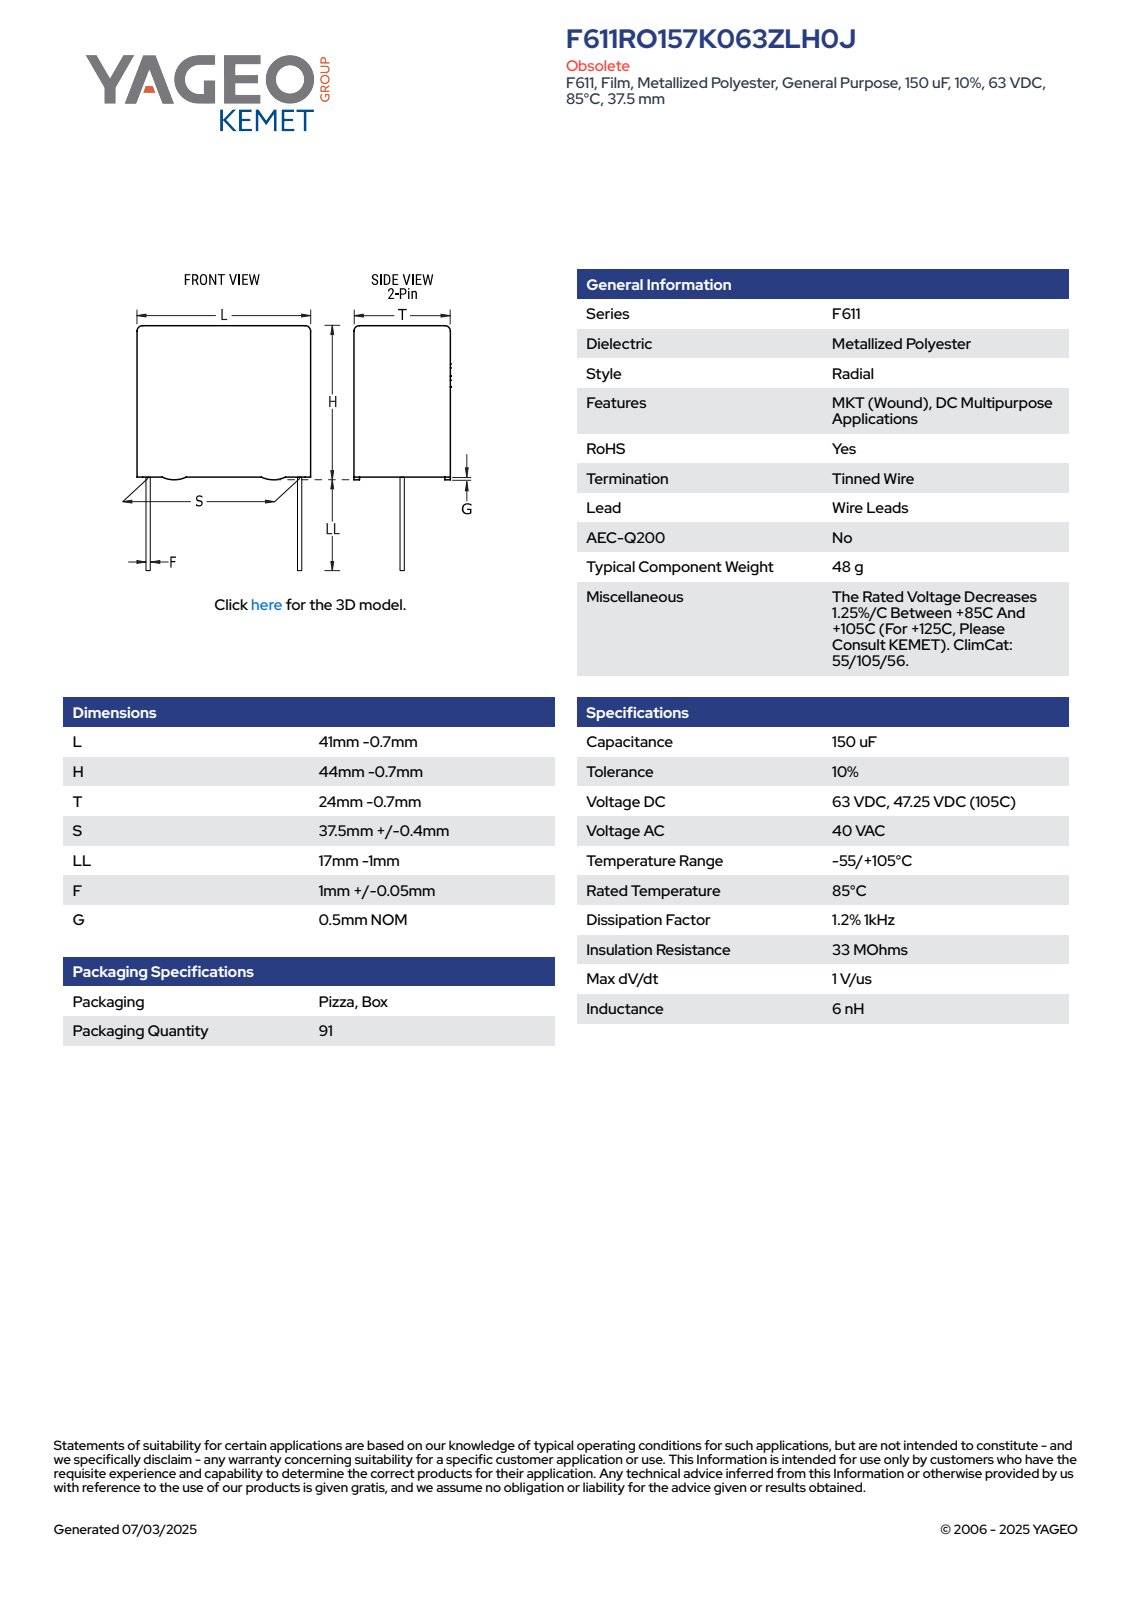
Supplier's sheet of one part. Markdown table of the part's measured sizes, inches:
| quantity | value |
| --- | --- |
| part name | CFR_RBG_41X44X24_L40.3H43.3T23.3S37.5LL16F1.05G0.5 |
| STEP written by | SolidWorks 2014 (AUTOMOTIVE_DESIGN) |
| units | inches |
| bodies | 4 solids, 89 faces (81 planar, 8 cylindrical, 0 other) |
| overall size | 2.335 × 1.587 × 0.917 |
| volume | 2.455 in³ |
| surface area | 11.79 in² |
| round bosses / shafts (diameter × count) | 0.041 × 2 |
| partial cylindrical surfaces (radius × count) | 0.02 × 4 |
| main face-to-face distances | 0.917, 1.587, 1.685, 0.918, 0.02, 1.705, 0.052, 0.865, 0.053, 0.813 |
